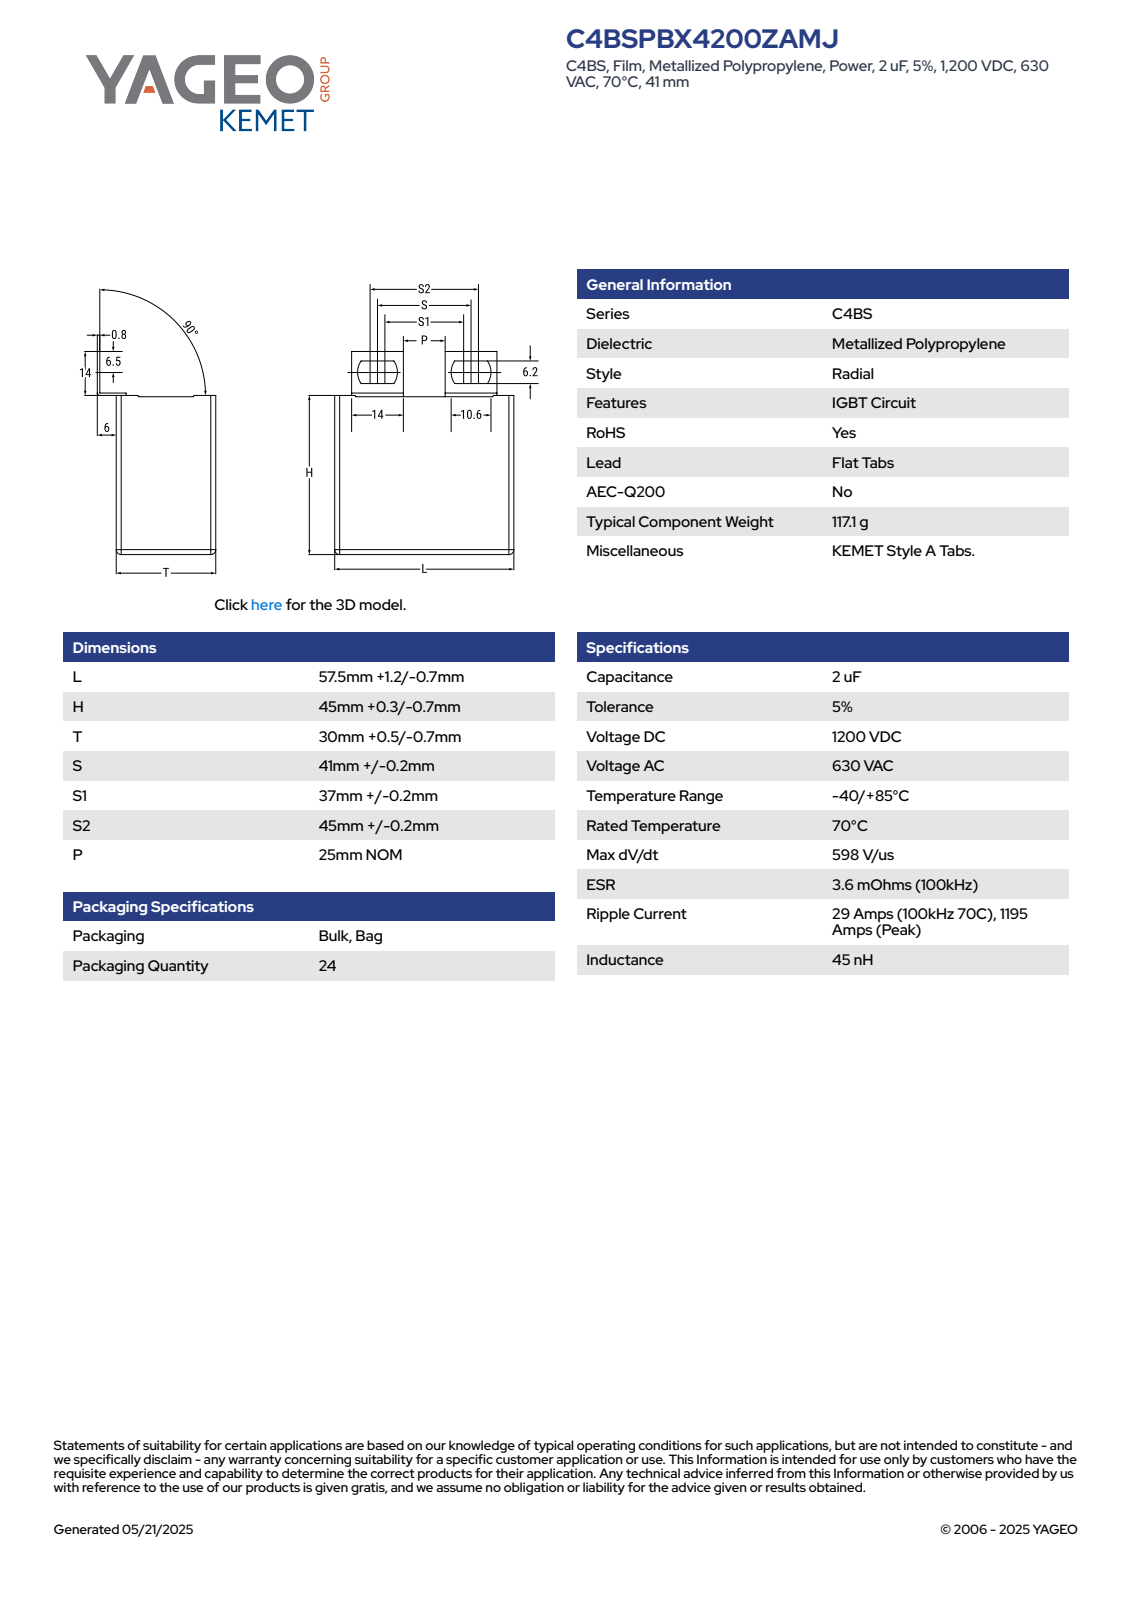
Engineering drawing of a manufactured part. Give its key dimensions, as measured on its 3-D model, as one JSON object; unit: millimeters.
{"part_name": "CFP_C4BA_57.5X45X30_L58.7H45.3T30.5S41.2", "step_written_by": "SolidWorks 2014 (AUTOMOTIVE_DESIGN)", "units": "millimeters", "bodies": {"solids": 4, "faces": 97, "planar": 91, "cylindrical": 6, "other": 0}, "overall_size": [59.9, 58.7, 36.51], "volume_mm3": 81456, "surface_area_mm2": 13586, "partial_cylinders_radius": [[6.1, 4]], "face_to_face_distances": [30.5, 45.25, 58.7, 0.6, 45.3, 45.9, 0.65, 36.5, 6, 35.9]}
